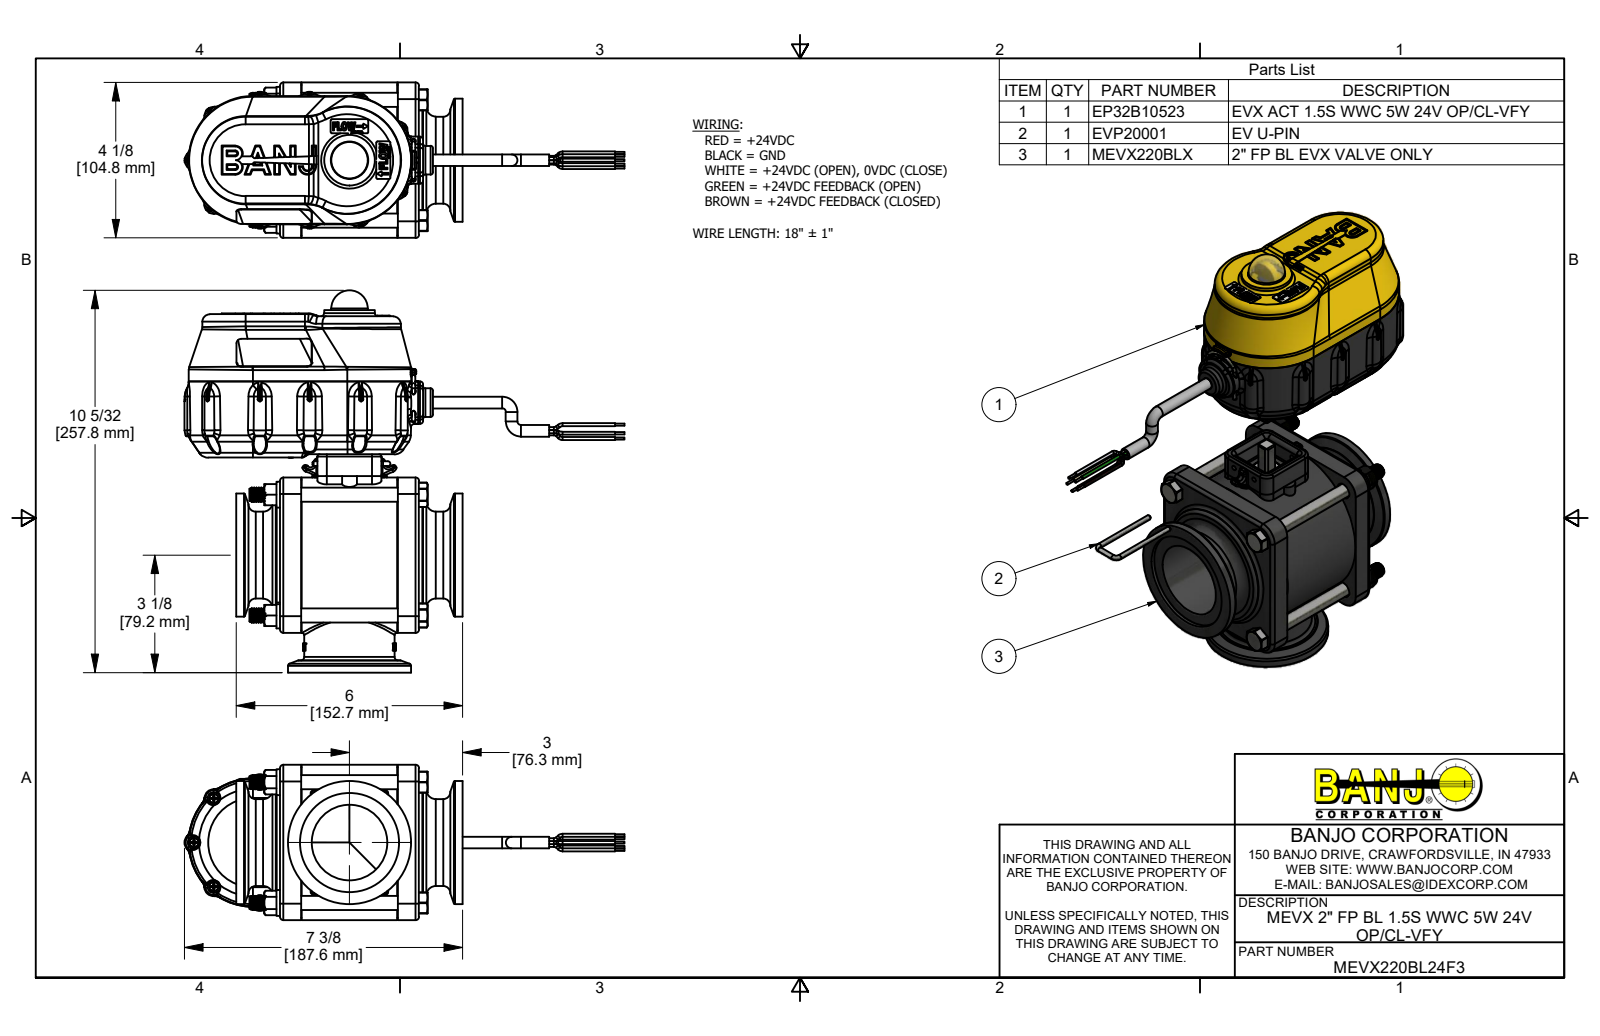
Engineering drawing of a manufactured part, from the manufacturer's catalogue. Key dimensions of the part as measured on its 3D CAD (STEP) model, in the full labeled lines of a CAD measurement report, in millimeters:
Part name (STEP PRODUCT): MEVX220BL24F3; EP32B10523; B61905PPHS; B632038PM (+8 more)
STEP written by: Autodesk Inventor 2019 (AUTOMOTIVE_DESIGN)
Units: millimetres
Bodies: 98 solids, 11705 faces (3239 planar, 3363 cylindrical, 5103 other)
Overall size (bounding box): 296.8 × 257.8 × 104.8
Volume: 1 624 000 mm³ · Surface area: 514 800 mm²
Round holes (diameter × count): ⌀2.4 ×11, ⌀3.8 ×11, ⌀2 ×7, ⌀2.7 ×4, ⌀3.2 ×4, ⌀3.5 ×4, ⌀3.8 ×4, ⌀3.8 ×4, ⌀4.3 ×4, ⌀7.8 ×4, ⌀9.8 ×4, ⌀11.1 ×4
Round bosses / shafts (diameter × count): ⌀8.2 ×60, ⌀2 ×25, ⌀6.4 ×17, ⌀3.6 ×11, ⌀2.7 ×11, ⌀2.2 ×11, ⌀1.5 ×10, ⌀9.5 ×5
Partial cylindrical surfaces — rounded edges, fillets, slot ends (radius × count): R0.3 ×180, R1 ×145, R0.3 ×84, R0.5 ×74, R0.1 ×53, R0.8 ×38, R2 ×28, R1.5 ×24
Main face-to-face distances: 2.5, 65.2, 1.5, 18.5, 16.4, 77.3, 63.1, 14.2, 79.5, 2.2
Hole centre spacings: 81.4, 57.5, 69, 38.4, 42.2, 62.4, 68.3, 72.4
